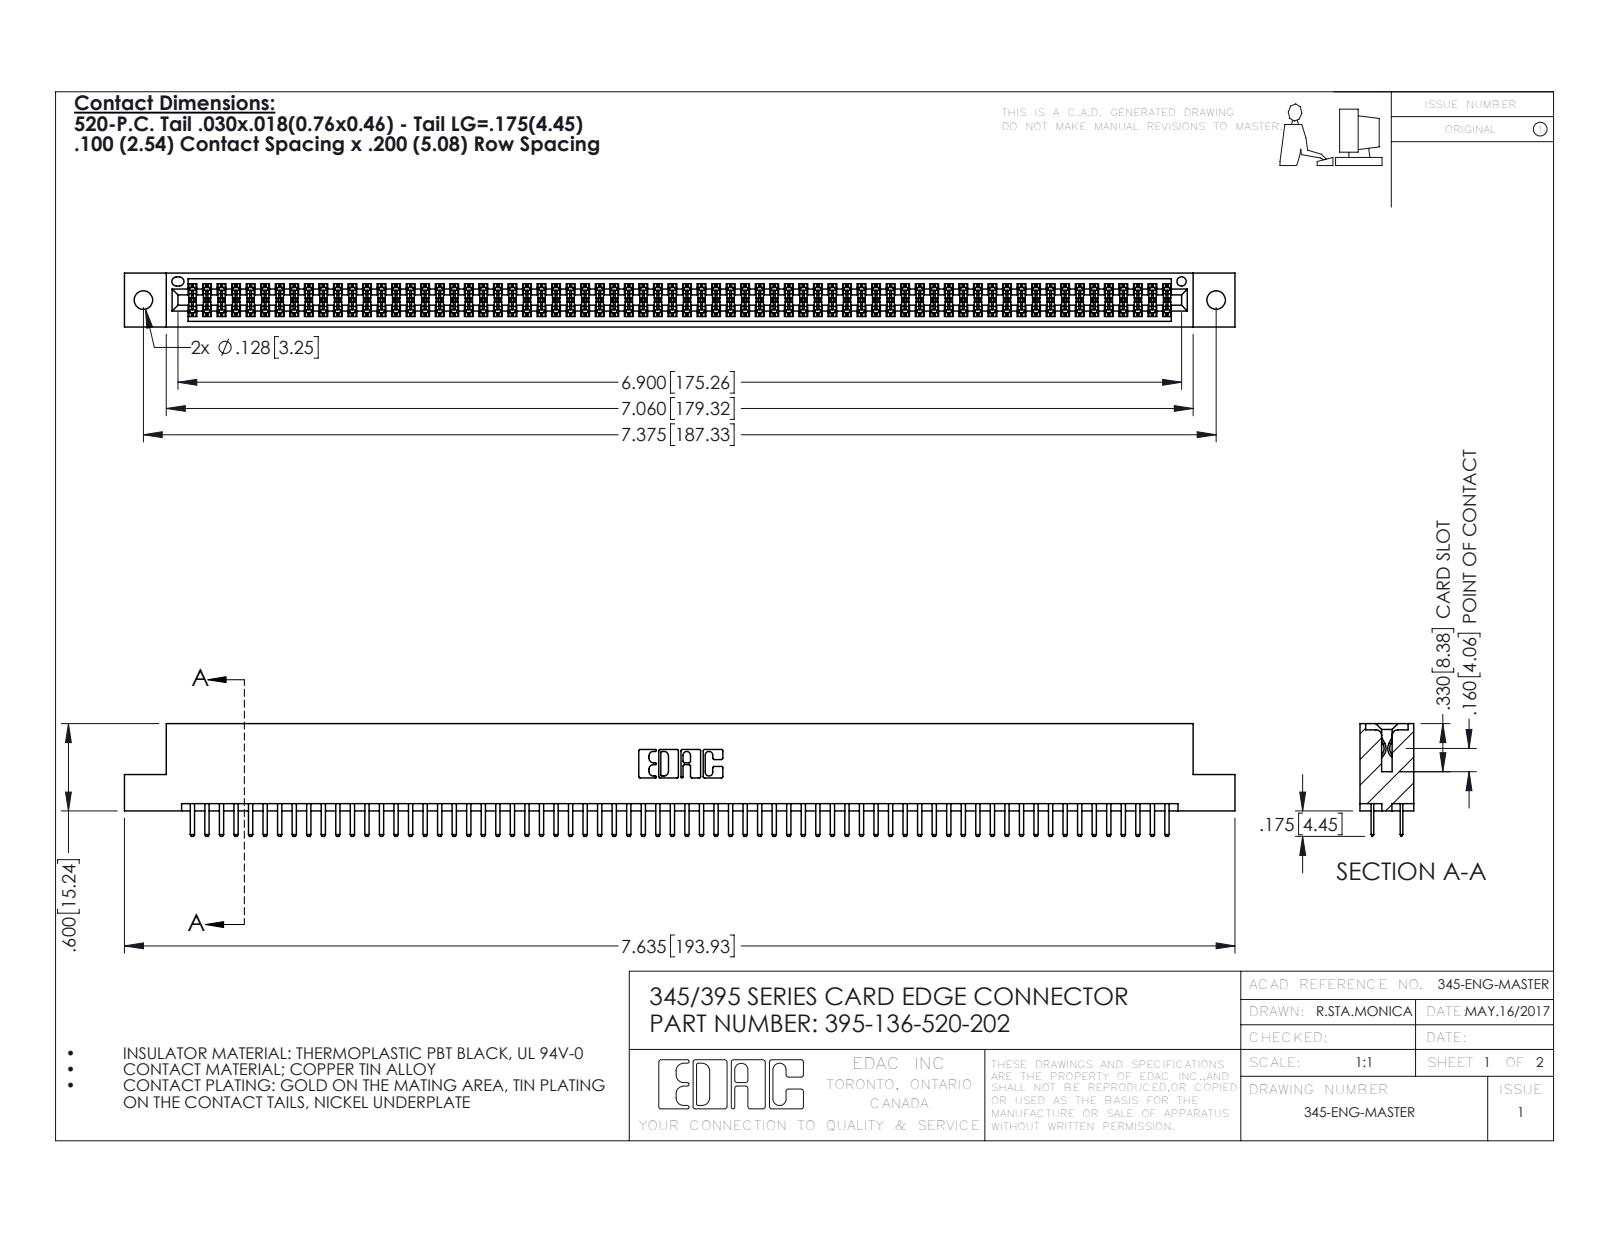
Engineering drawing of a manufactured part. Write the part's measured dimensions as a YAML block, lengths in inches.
part_name: "345-292-001_345-293-120; 395-136-520-202; 345 Part_Flush Mounting Lugs - 0.128 Dia"
step_written_by: "SolidWorks 2016 (CONFIG_CONTROL_DESIGN)"
units: inches
bodies: {solids: 137, faces: 7470, planar: 4840, cylindrical: 2630, other: 0}
overall_size: [7.635, 0.775, 0.37]
volume: 1.158
surface_area: 43.65
round_holes:
  - {diameter: 0.128, count: 2}
  - {diameter: 0.064, count: 1}
partial_cylinders:
  - {radius: 0.006, count: 204}
  - {radius: 0.01, count: 140}
  - {radius: 0.01, count: 22}
  - {radius: 0.007, count: 6}
  - {radius: 0.031, count: 6}
  - {radius: 0.026, count: 3}
  - {radius: 0.014, count: 2}
  - {radius: 0.019, count: 2}
face_to_face_distances: [0.298, 0.072, 0.2, 0.37, 0.098, 0.272, 0.025, 0.225, 0.022, 0.072]
hole_center_spacings: [0.27, 7.139, 7.375]
